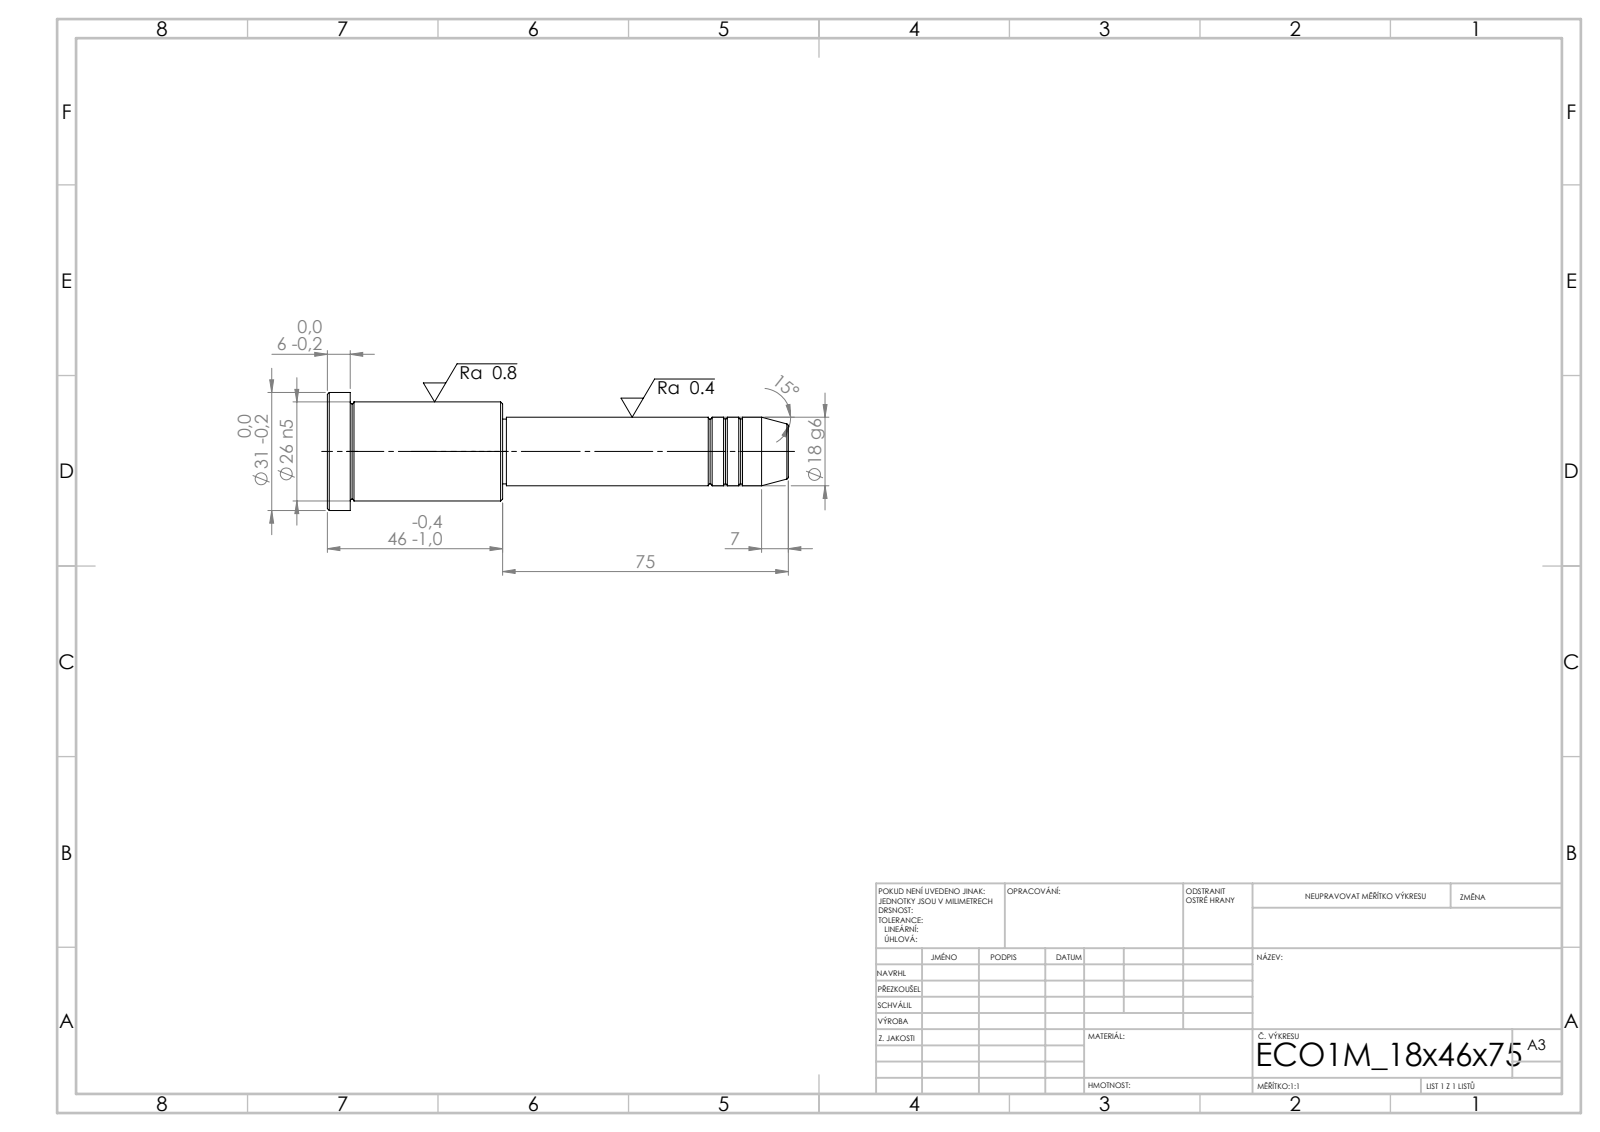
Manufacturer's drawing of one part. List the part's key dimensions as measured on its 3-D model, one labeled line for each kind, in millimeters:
STEP written by: SolidWorks 2019 (CONFIG_CONTROL_DESIGN)
Units: millimetres
Bodies: 1 solid, 43 faces (5 planar, 14 cylindrical, 24 other)
Overall size (bounding box): 121 × 31 × 31
Volume: 44 358 mm³ · Surface area: 9 603 mm²
Round bosses / shafts (diameter × count): ⌀31 ×1, ⌀26 ×1, ⌀18 ×1, ⌀17 ×1
Main face-to-face distances: 46, 40, 6, 75, 115, 121, 74, 1, 41, 47
